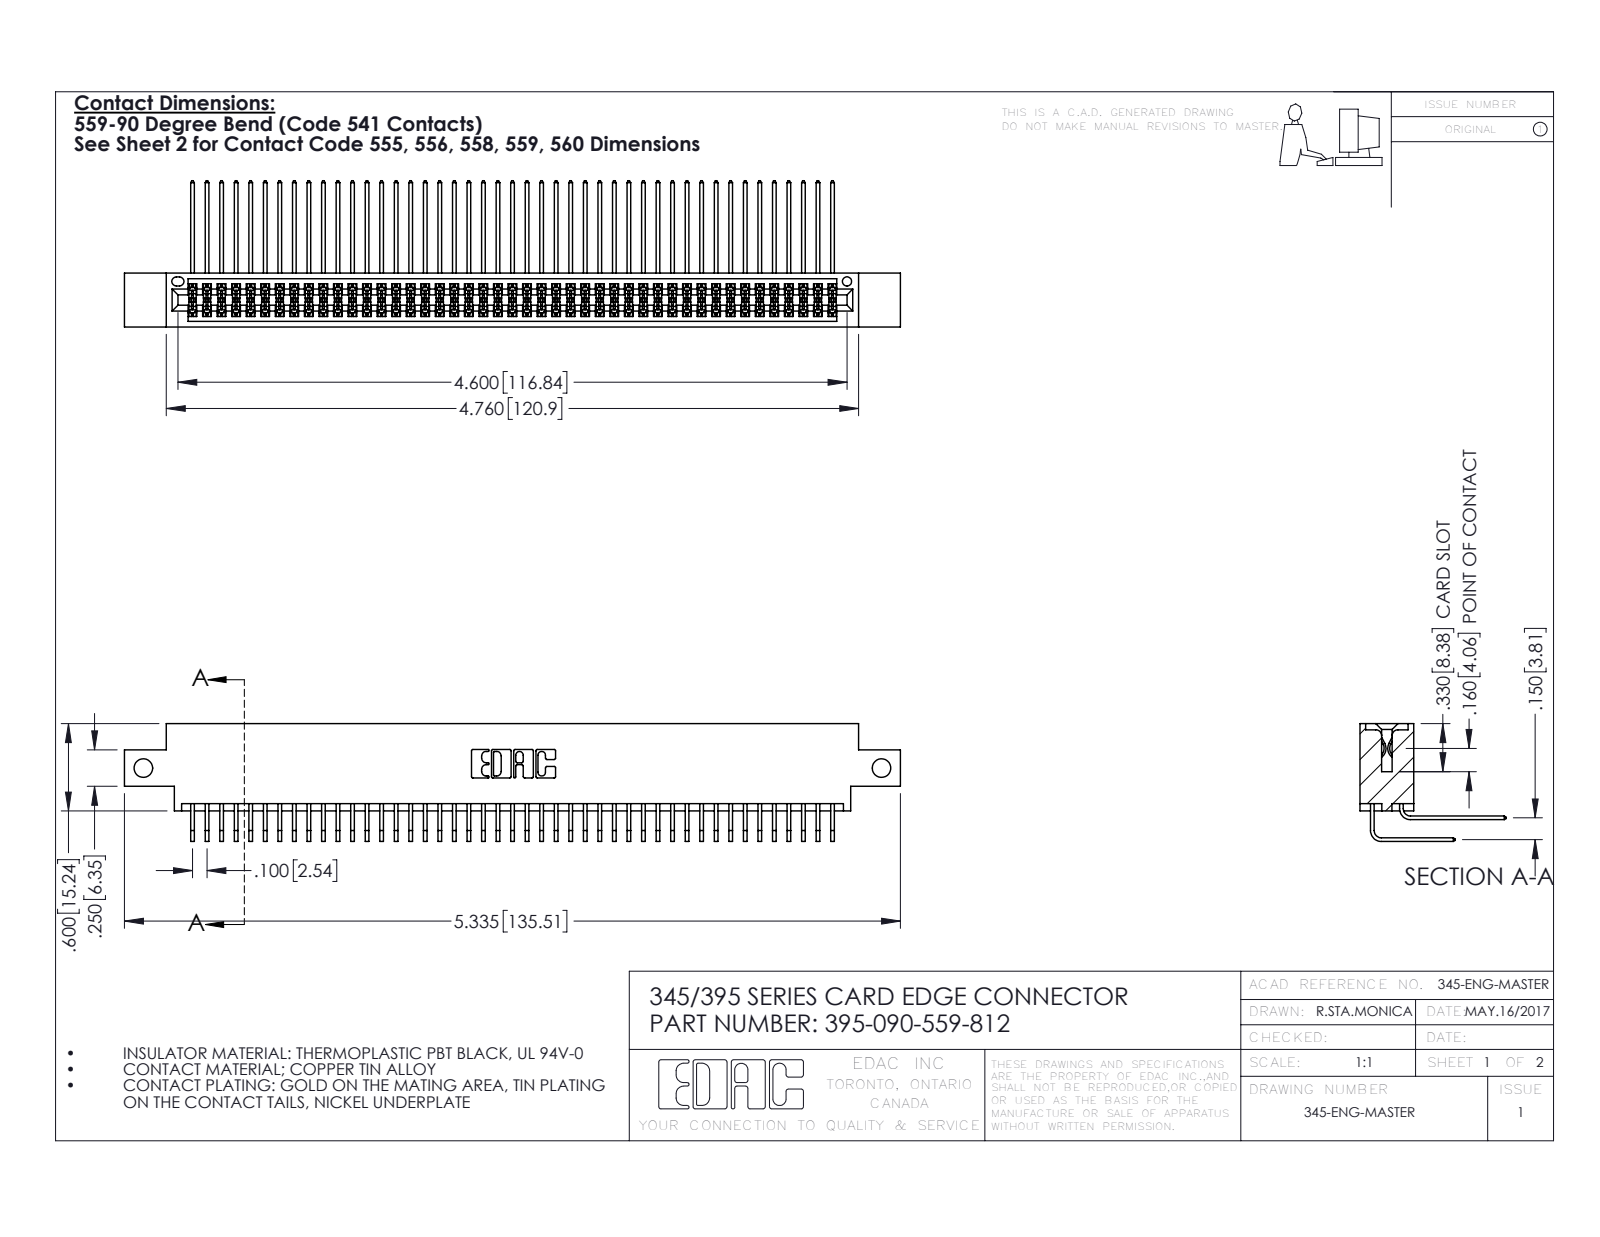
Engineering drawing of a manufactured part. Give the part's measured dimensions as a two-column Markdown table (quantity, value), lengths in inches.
| quantity | value |
| --- | --- |
| part name | 345 Part_0.170 Offset - Side Mount; 395-090-559-812; 345-292-001_559 Tail - 2; 345-292-001_558 559 Tail - 1 |
| STEP written by | SolidWorks 2016 (CONFIG_CONTROL_DESIGN) |
| units | inches |
| bodies | 91 solids, 4810 faces (3234 planar, 1576 cylindrical, 0 other) |
| overall size | 5.335 × 1.005 × 0.809 |
| volume | 0.824 in³ |
| surface area | 34.84 in² |
| round holes (diameter × count) | 0.128 × 2, 0.064 × 1 |
| partial cylindrical surfaces (radius × count) | 0.006 × 135, 0.01 × 22, 0.007 × 6, 0.031 × 6, 0.026 × 3, 0.014 × 2, 0.019 × 2, 0.022 × 2 |
| main face-to-face distances | 0.072, 0.298, 0.37, 0.2, 0.098, 0.272, 0.025, 0.225, 0.175, 0.15 |
| hole center spacings | 5.075 |
